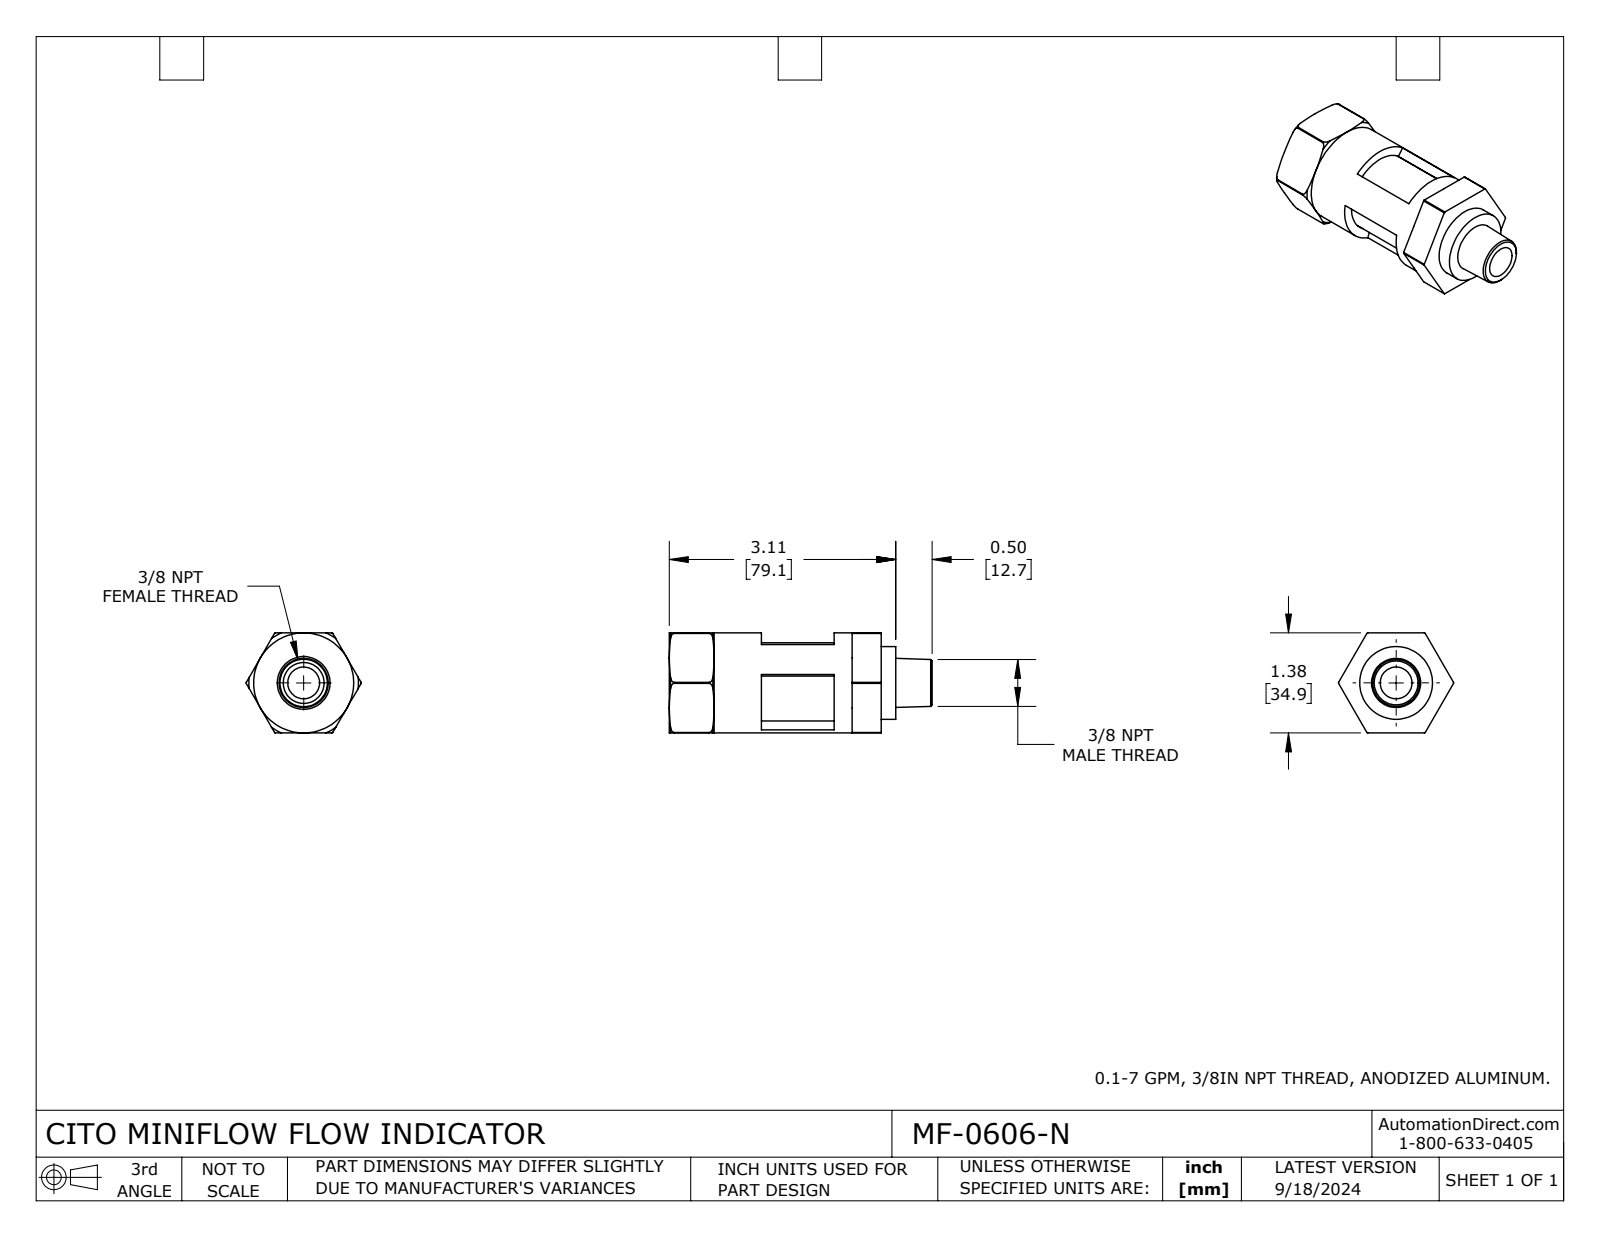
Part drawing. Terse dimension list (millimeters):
name: MF-0606-N
written by: SolidWorks 2023 (CONFIG_CONTROL_DESIGN)
unit: mm
bodies: 2 solids, 102 faces (40 planar, 28 cylindrical, 34 other)
size: 91.8 × 40.1 × 34.9
volume: 45 870 mm³; area: 21 900 mm²
holes: 1× ⌀11.1, 1× ⌀14.3, 1× ⌀22.4, 1× ⌀28.2
bosses: 1× ⌀34.9, 1× ⌀28, 1× ⌀25.4
rounds: 1× R20.1
face distances: 34.9, 63.9, 10.2, 74, 58.4, 48.2, 15.7, 11.6, 46.8, 5.1
